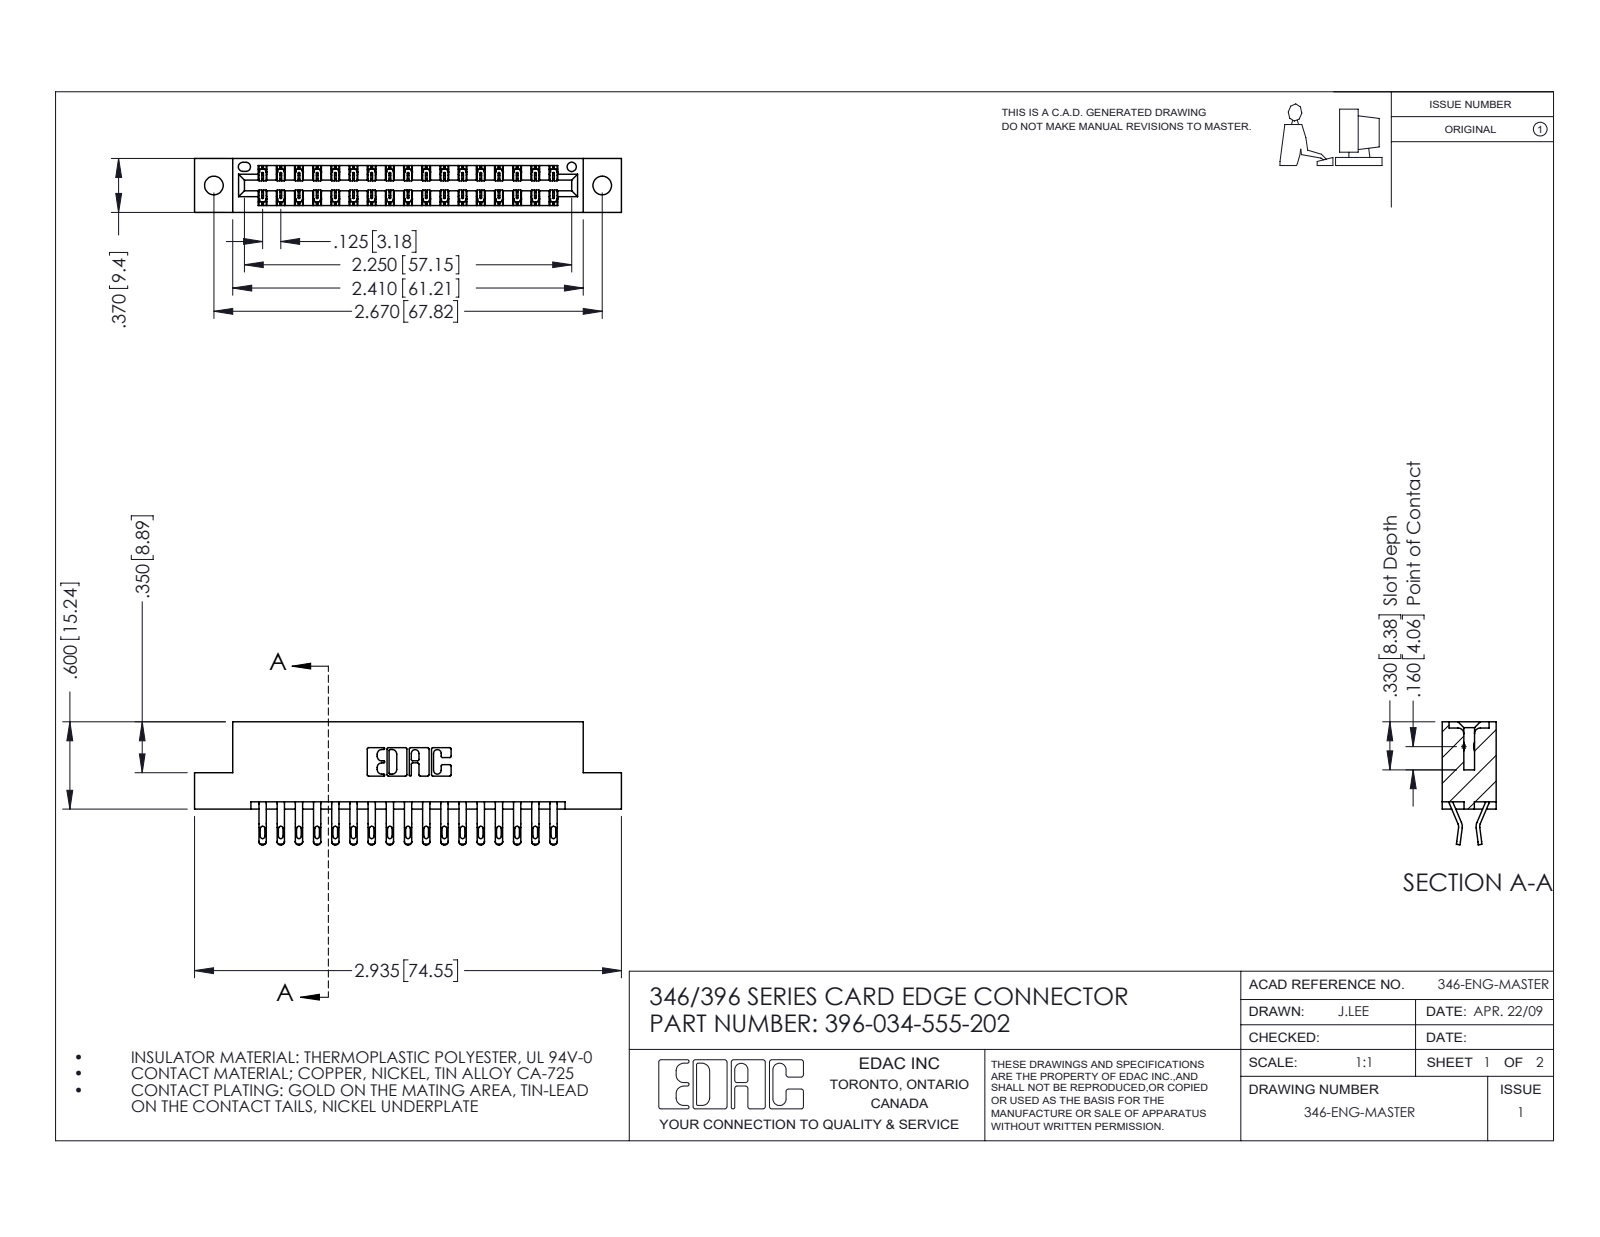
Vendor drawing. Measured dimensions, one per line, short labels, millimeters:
name: 396-034-555-202; 346 Part_Flush Mounting Lugs - 0.128 Dia; 345-292-001_555 Tail
written by: SolidWorks 2016 (CONFIG_CONTROL_DESIGN)
unit: mm
bodies: 35 solids, 2094 faces (1198 planar, 896 cylindrical, 0 other)
size: 74.5 × 21.5 × 9.4
volume: 7 140 mm³; area: 9 497 mm²
holes: 2× ⌀3.3, 1× ⌀1.6
rounds: 68× R0.4, 68× R0.5, 51× R0.2, 22× R0.3, 6× R0.2, 6× R0.8, 3× R0.7, 2× R0.3
face distances: 1.2, 8.2, 6.4, 9.4, 0.6, 1.8, 7.6, 7, 3.8, 5.6
hole spacings: 6.2, 62.6, 67.8
